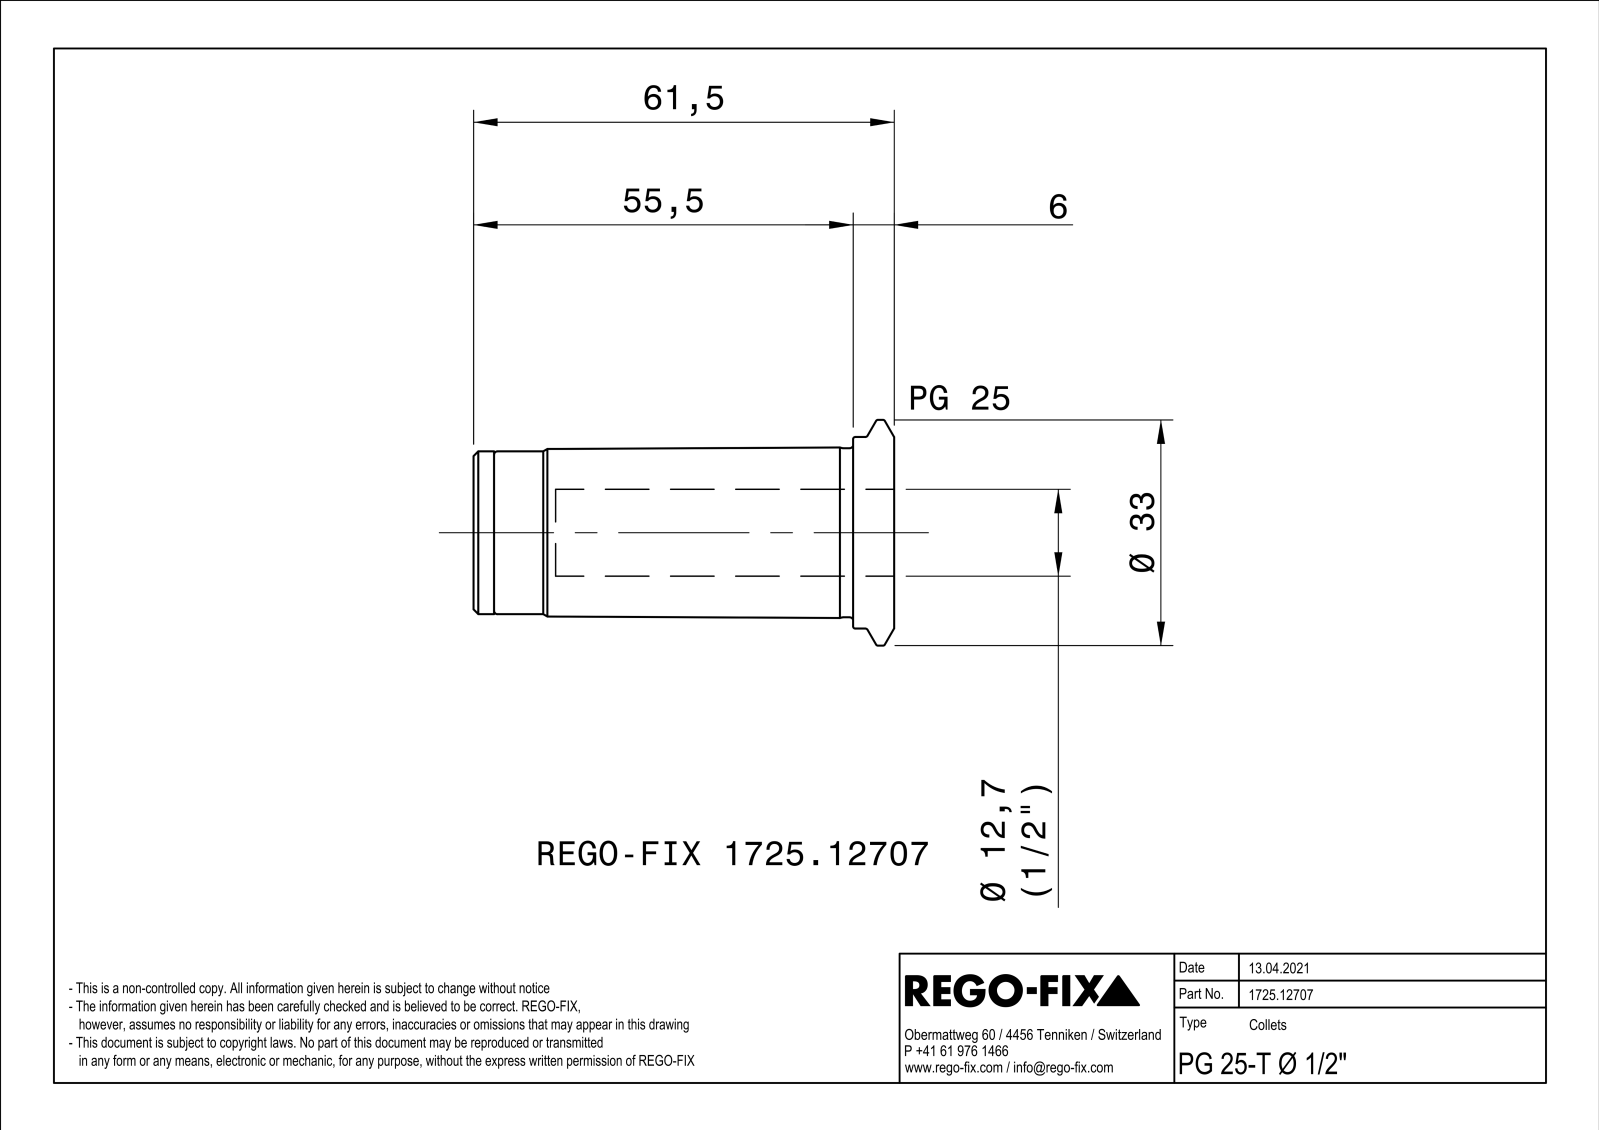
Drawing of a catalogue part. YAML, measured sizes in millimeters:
part_name: "NOCUT"
step_written_by: "SIEMENS PLM Software Solid Edge ST10 (AUTOMOTIVE_DESIGN)"
units: millimeters
bodies: {solids: 0, faces: 86, planar: 24, cylindrical: 22, other: 40}
overall_size: [58.5, 33, 32.94]
round_holes:
  - {diameter: 3.24, count: 1}
  - {diameter: 4.3, count: 1}
  - {diameter: 12.7, count: 1}
  - {diameter: 21, count: 1}
  - {diameter: 22, count: 1}
round_bosses_or_shafts:
  - {diameter: 33, count: 1}
  - {diameter: 28, count: 1}
  - {diameter: 24.7, count: 1}
  - {diameter: 23.8, count: 1}
partial_cylinders:
  - {radius: 0.5, count: 2}
  - {radius: 4.06, count: 1}
  - {radius: 4.17, count: 1}
face_to_face_distances: [1, 6, 55.9, 57, 49.9, 51, 1.1, 58.5, 52.5, 2.6]
